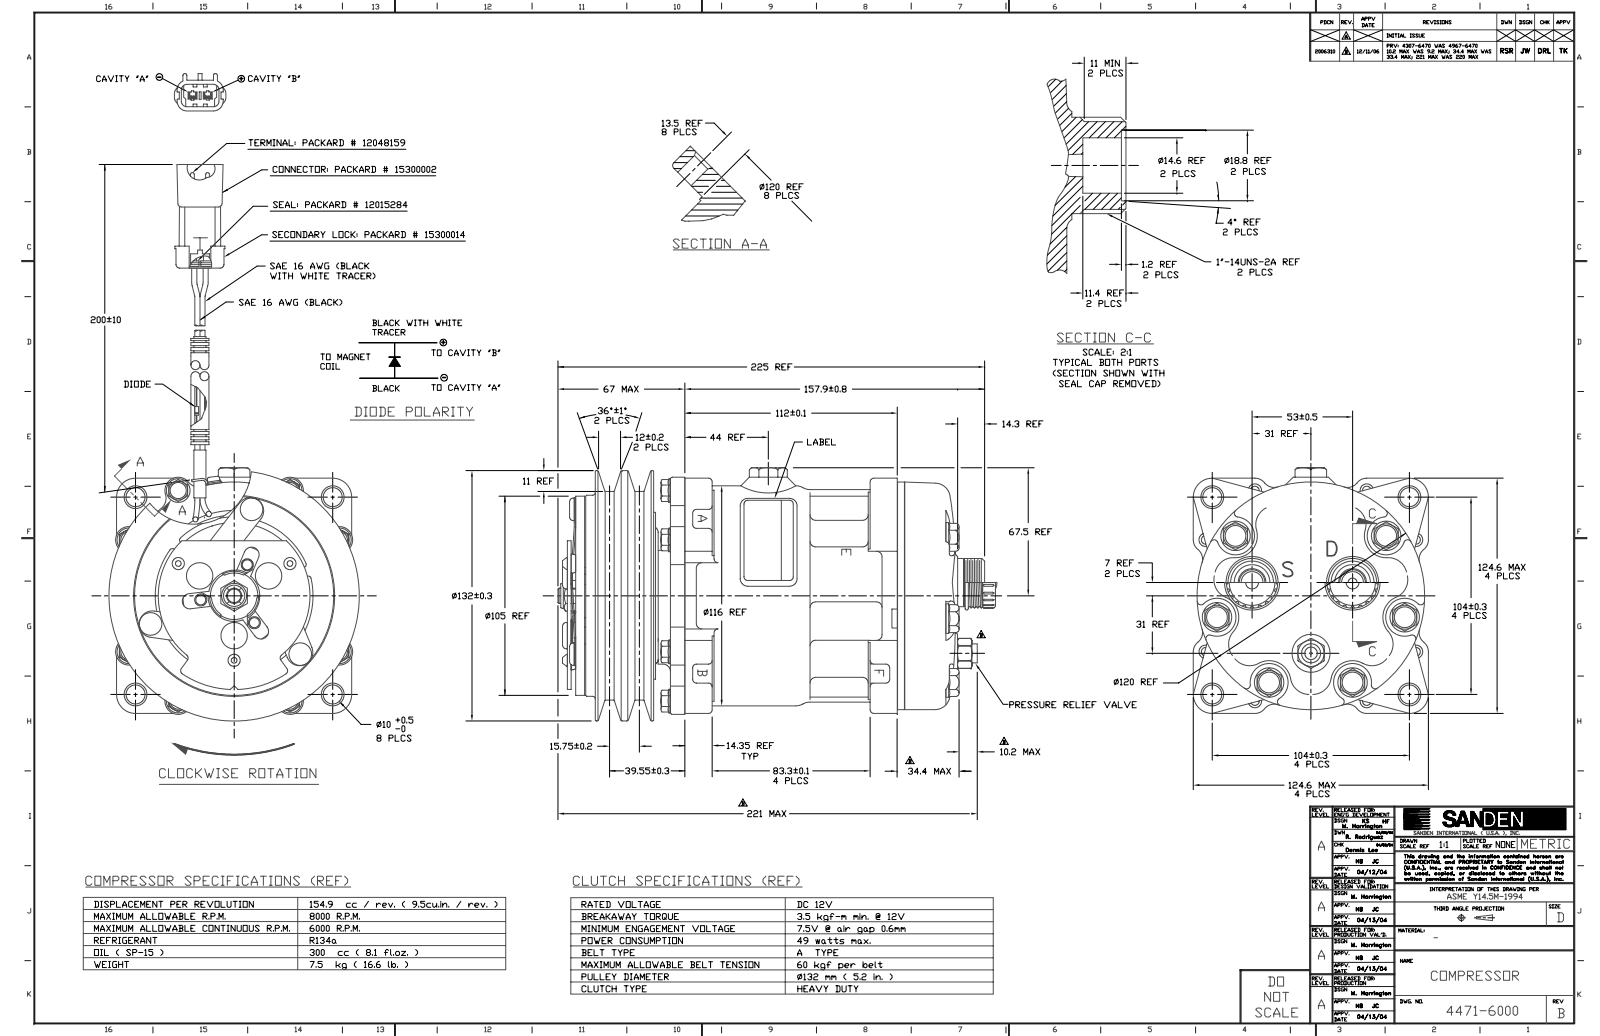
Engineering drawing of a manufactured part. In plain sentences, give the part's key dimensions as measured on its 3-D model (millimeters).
The part is named "SANDEN_4471_REV_C_COMPR_AC1". Its 3-D file was written by "SolidWorks 2007 (CONFIG_CONTROL_DESIGN)". It is 1 solid with 2556 faces: 746 planar, 787 cylindrical and 1023 other. Overall it measures 327.93 by 224.94 by 132 millimeters. Its volume is 2 115 000 cubic millimeters and its surface area 251 563 square millimeters. Round holes: 8 of diameter 5.5, 8 of diameter 8.5, 6 of diameter 11.29, 4 of diameter 10.25, 3 of diameter 2.2, 3 of diameter 5.08, 3 of diameter 6.6, 3 of diameter 8, 2 of diameter 3, 2 of diameter 12, 2 of diameter 14.6, 1 of diameter 3.5. Round bosses or shafts: 12 of diameter 2.7, 8 of diameter 12.9, 4 of diameter 12, 3 of diameter 14, 3 of diameter 10, 3 of diameter 7.9, 3 of diameter 6.5, 3 of diameter 6.4. Partial cylindrical surfaces (rounded edges, fillets, slot ends): 37 of radius 2, 33 of radius 7, 27 of radius 1, 24 of radius 3, 24 of radius 6.5, 22 of radius 0.5, 22 of radius 5, 16 of radius 4. The main face-to-face distances are 5.6, 5, 36.24, 8.71, 44.95, 0.8, 37.64, 50.55, 41.84, 2. The hole center spacings are 22.77, 62.85, 81.58, 88.89, 109.83, 134.9, 46.4, 36.77.
